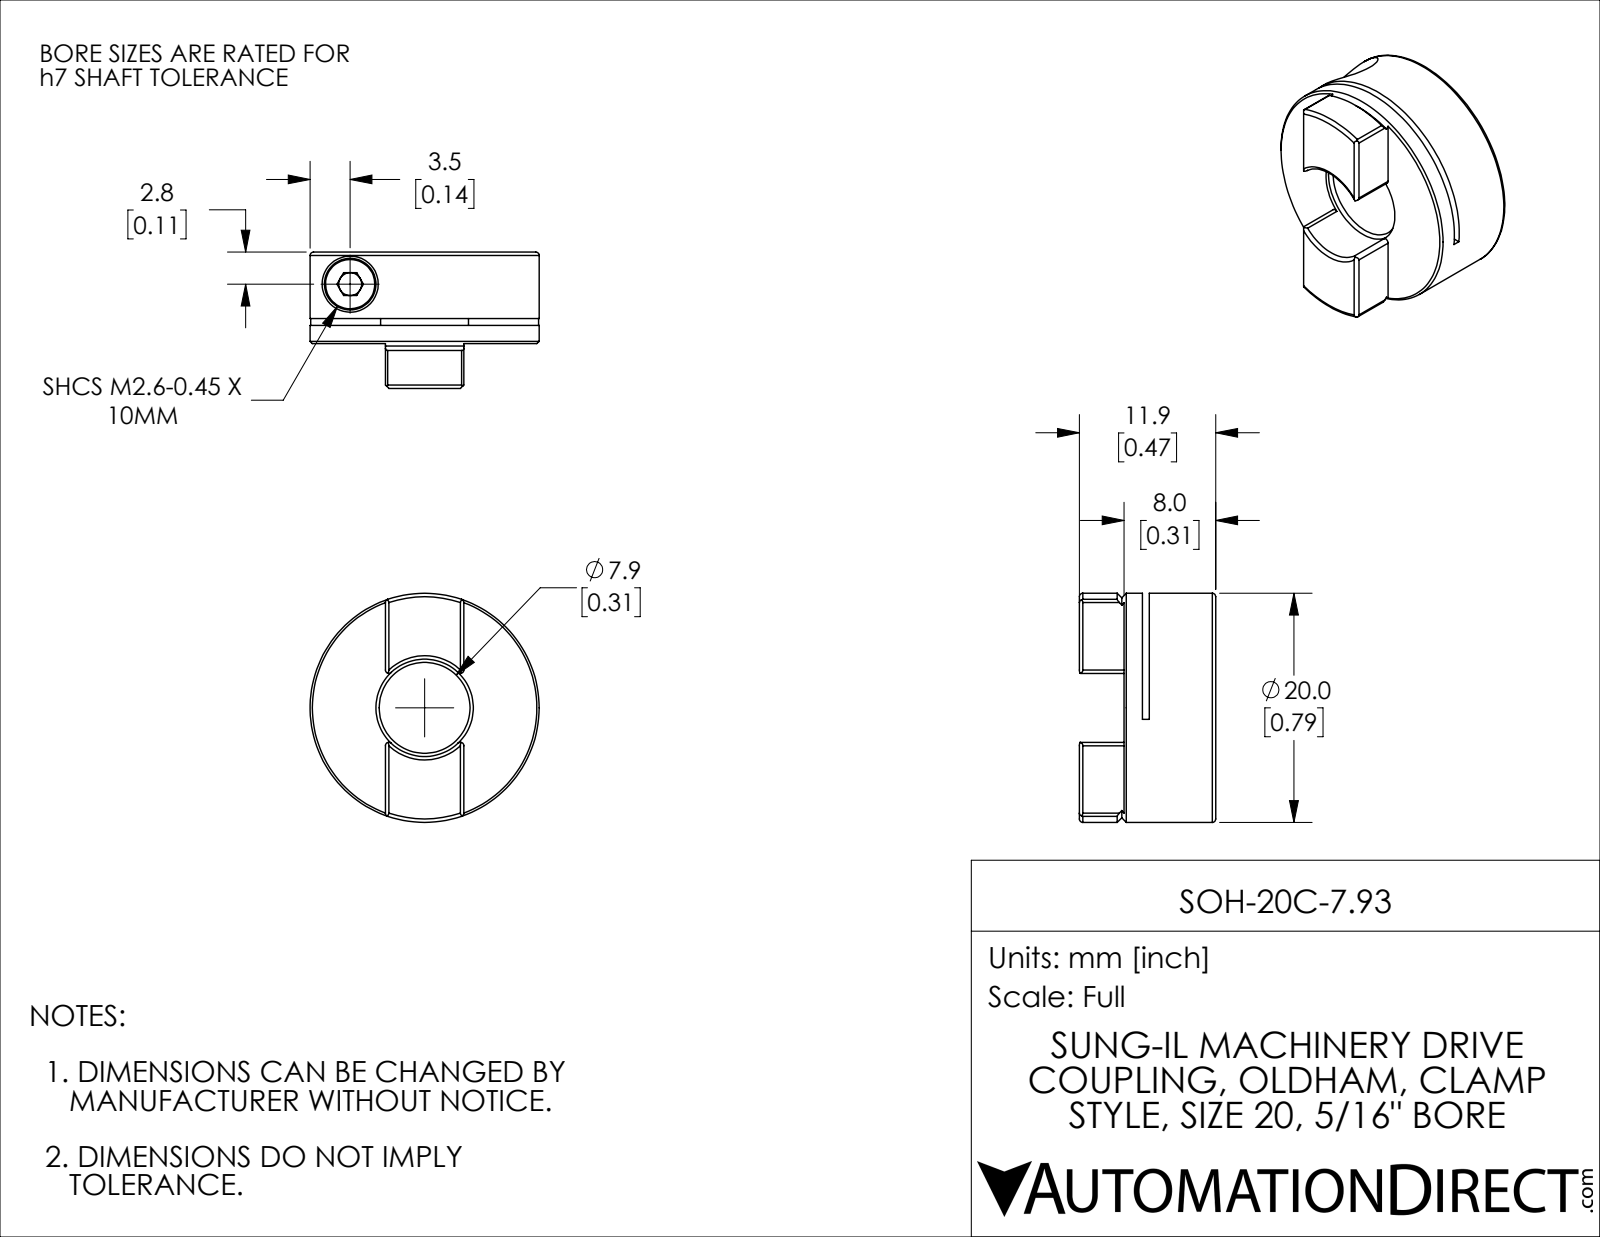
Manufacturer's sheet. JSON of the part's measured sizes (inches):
{"part_name": "SOH-20C-7.93", "step_written_by": "SolidWorks 2021 (CONFIG_CONTROL_DESIGN)", "units": "inches", "bodies": {"solids": 2, "faces": 97, "planar": 38, "cylindrical": 33, "other": 26}, "overall_size": [0.787, 0.787, 0.469], "volume_in3": 0.137, "surface_area_in2": 3.117, "round_holes": [[0.079, 1], [0.081, 1], [0.11, 1], [0.193, 1], [0.312, 1], [0.335, 1]], "round_bosses_or_shafts": [[0.787, 1], [0.177, 1], [0.102, 1]], "partial_cylinders_radius": [[0.012, 8], [0.886, 1]], "face_to_face_distances": [0.315, 0.228, 0.252, 0.063, 0.024, 0.087, 0.469, 0.24, 0.217, 0.154]}
